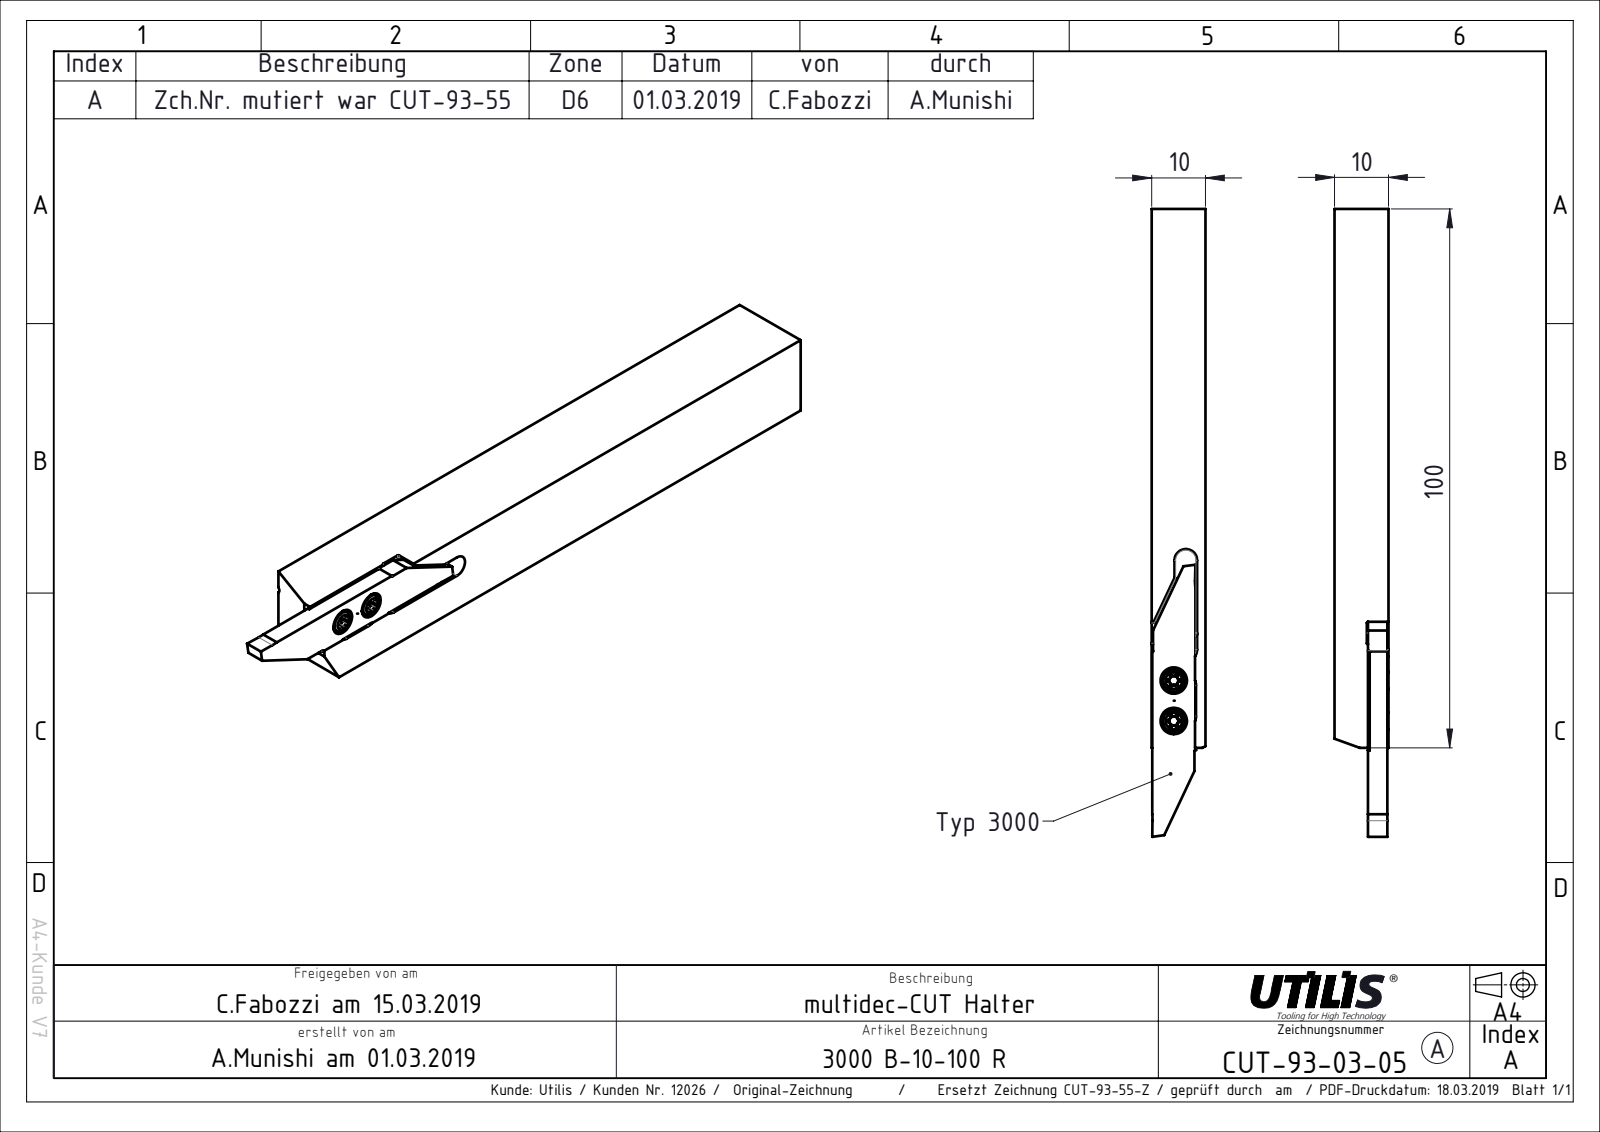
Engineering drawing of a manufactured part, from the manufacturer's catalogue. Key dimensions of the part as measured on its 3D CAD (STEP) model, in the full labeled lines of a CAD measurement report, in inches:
Part name (STEP PRODUCT): CUT-93-Kunde_55; CUT-93-Kunde; CUT-Vorlage 3000 R+L Lang Kunde_R-Lang; CUT-93-55 (+1 more)
STEP written by: SolidWorks 2015 (CONFIG_CONTROL_DESIGN)
Units: inches
Bodies: 2 solids, 55 faces (36 planar, 19 cylindrical, 0 other)
Overall size (bounding box): 4.587 × 0.394 × 0.394
Volume: 0.607 in³ · Surface area: 8.389 in²
Round holes (diameter × count): ⌀0.098 ×2, ⌀0.193 ×2
Partial cylindrical surfaces — rounded edges, fillets, slot ends (radius × count): R0.083 ×4, R0.006 ×2, R0.394 ×2
Main face-to-face distances: 0.394, 0.15, 0.244, 0.142, 0.386, 0.079, 0.315, 0.061, 0.018, 0.333
Hole centre spacings: 0.148, 0.295
